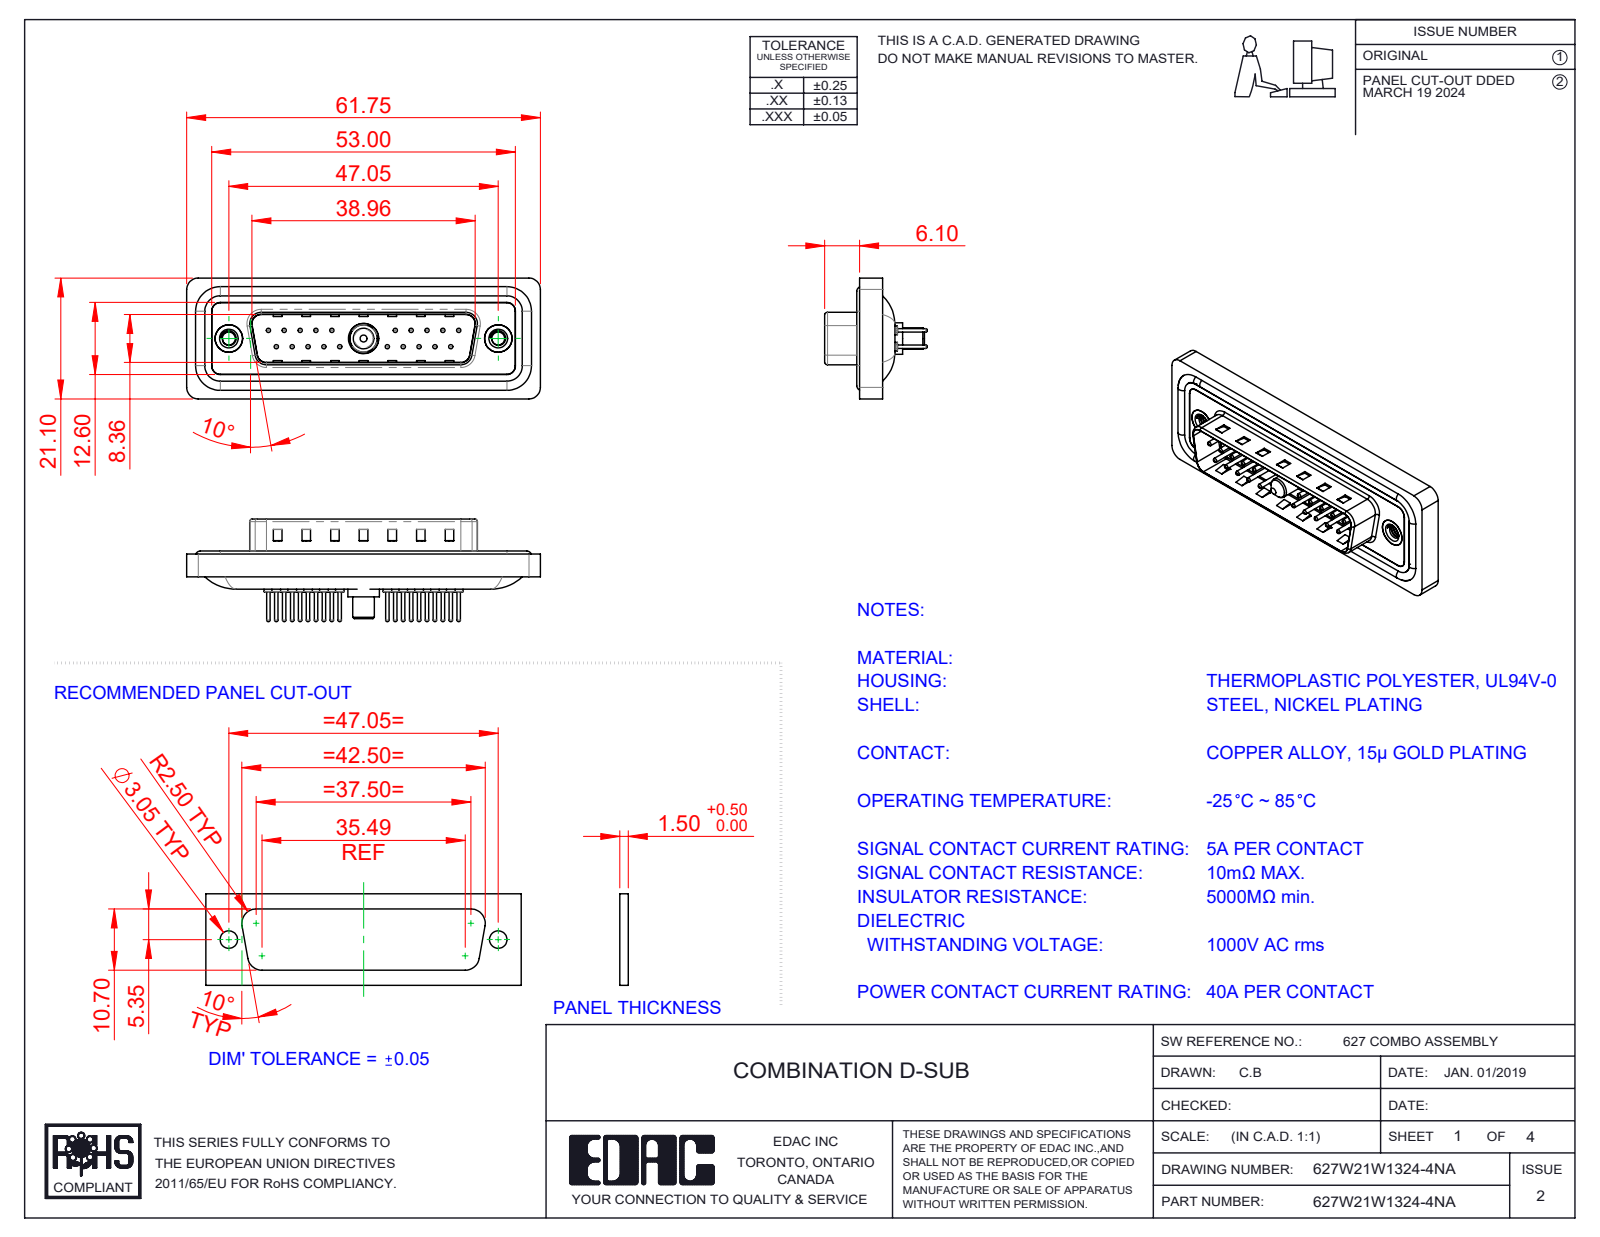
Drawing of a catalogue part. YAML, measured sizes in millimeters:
part_name: "Power Pin_40A S; 627Combo Shell Rear_25 Contacts; 627Combo Contact Row 1_24; 627Combo Waterproof Housing_25 Contacts (+5 more)"
step_written_by: "SolidWorks 2023 (CONFIG_CONTROL_DESIGN)"
units: millimeters
bodies: {solids: 29, faces: 1260, planar: 359, cylindrical: 489, other: 412}
overall_size: [61.75, 21.1, 17.9]
volume: 7218
surface_area: 11962
round_holes:
  - {diameter: 0.75, count: 20}
  - {diameter: 1.6, count: 20}
  - {diameter: 2, count: 20}
  - {diameter: 2.26, count: 2}
  - {diameter: 4, count: 2}
  - {diameter: 4.8, count: 2}
  - {diameter: 5, count: 2}
  - {diameter: 4.85, count: 1}
  - {diameter: 5.3, count: 1}
round_bosses_or_shafts:
  - {diameter: 1.5, count: 20}
  - {diameter: 0.6, count: 20}
  - {diameter: 1.6, count: 4}
  - {diameter: 4.9, count: 2}
  - {diameter: 5.5, count: 1}
  - {diameter: 5.2, count: 1}
  - {diameter: 4.75, count: 1}
  - {diameter: 3.75, count: 1}
partial_cylinders:
  - {radius: 1.5, count: 22}
  - {radius: 2, count: 18}
  - {radius: 0.5, count: 8}
  - {radius: 1.6, count: 8}
  - {radius: 0.25, count: 4}
  - {radius: 0.6, count: 4}
  - {radius: 0.65, count: 4}
  - {radius: 0.9, count: 4}
face_to_face_distances: [0.4, 1.5, 1.1, 1.6, 0.5, 3.1, 2.9, 4.1, 0.82, 9.58]
hole_center_spacings: [3.16, 2.77, 5.54, 8.31, 5.04, 19.39, 20.97, 22.16]
